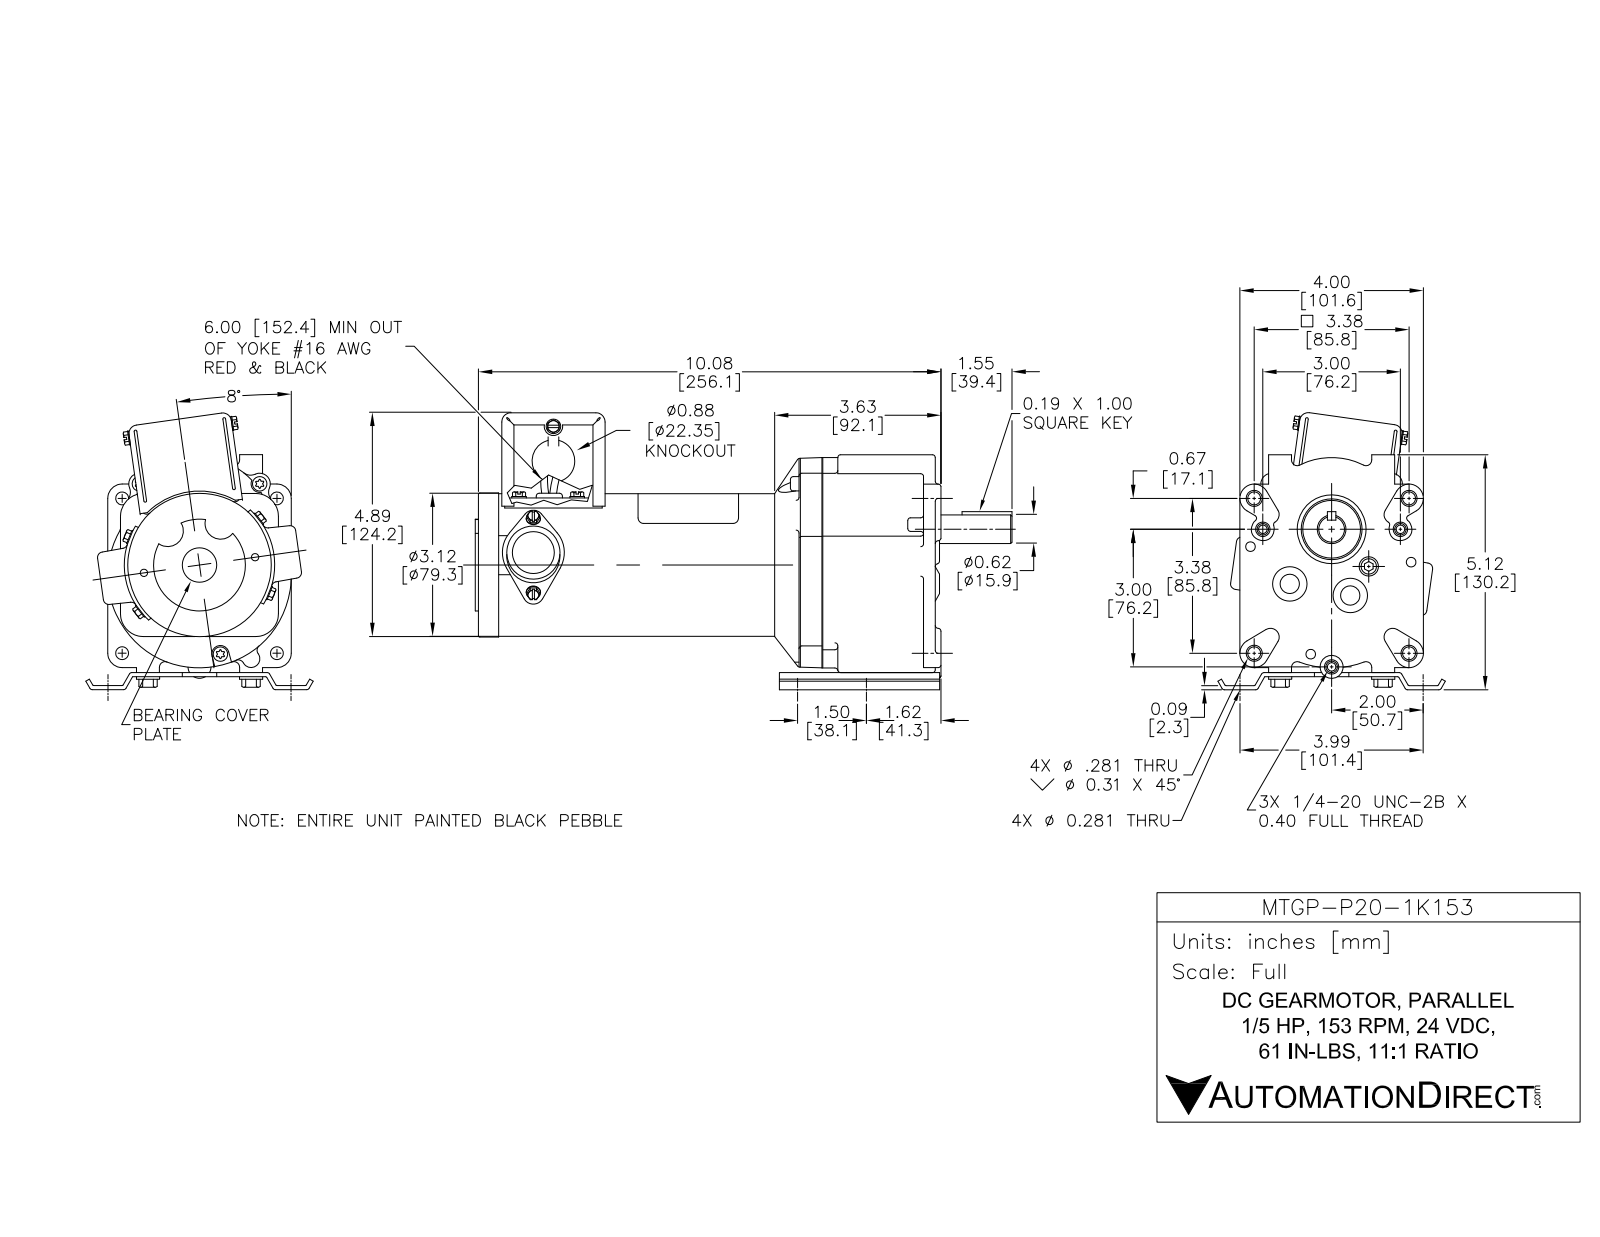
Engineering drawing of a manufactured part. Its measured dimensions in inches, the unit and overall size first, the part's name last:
Units: inches
Overall size (bounding box): 11.698 × 6.209 × 4.939
Round holes (diameter × count): ⌀0.3 ×11, ⌀0.5 ×5, ⌀0.25 ×4, ⌀0.345 ×4, ⌀0.21 ×3, ⌀0.125 ×2, ⌀0.198 ×2, ⌀0.208 ×2, ⌀0.345 ×2, ⌀0.375 ×1, ⌀0.46 ×1, ⌀0.625 ×1
Round bosses / shafts (diameter × count): ⌀0.314 ×5, ⌀0.3 ×4, ⌀0.208 ×3, ⌀0.46 ×2, ⌀0.1 ×2, ⌀3.156 ×1, ⌀1.325 ×1, ⌀0.625 ×1
Partial cylindrical surfaces — rounded edges, fillets, slot ends (radius × count): R0.019 ×28, R0.1 ×23, R0.025 ×8, R0.25 ×7, R0.159 ×4, R0.19 ×4, R0.191 ×4, R0.234 ×4
Main face-to-face distances: 1.375, 3.495, 2.12, 0.09, 0.031, 0.25, 0.063, 0.05, 1.425, 3.545
Hole centre spacings: 1.62, 1.23, 1.5, 1.504, 1.603, 2.974, 3.375, 6.911
Volume: 65.11 in³ · Surface area: 470.6 in²
Bodies: 53 solids, 984 faces (567 planar, 365 cylindrical, 52 other)
Part name (STEP PRODUCT): MTGP-P20-1K153
STEP written by: SolidWorks 2014 (AUTOMOTIVE_DESIGN)
